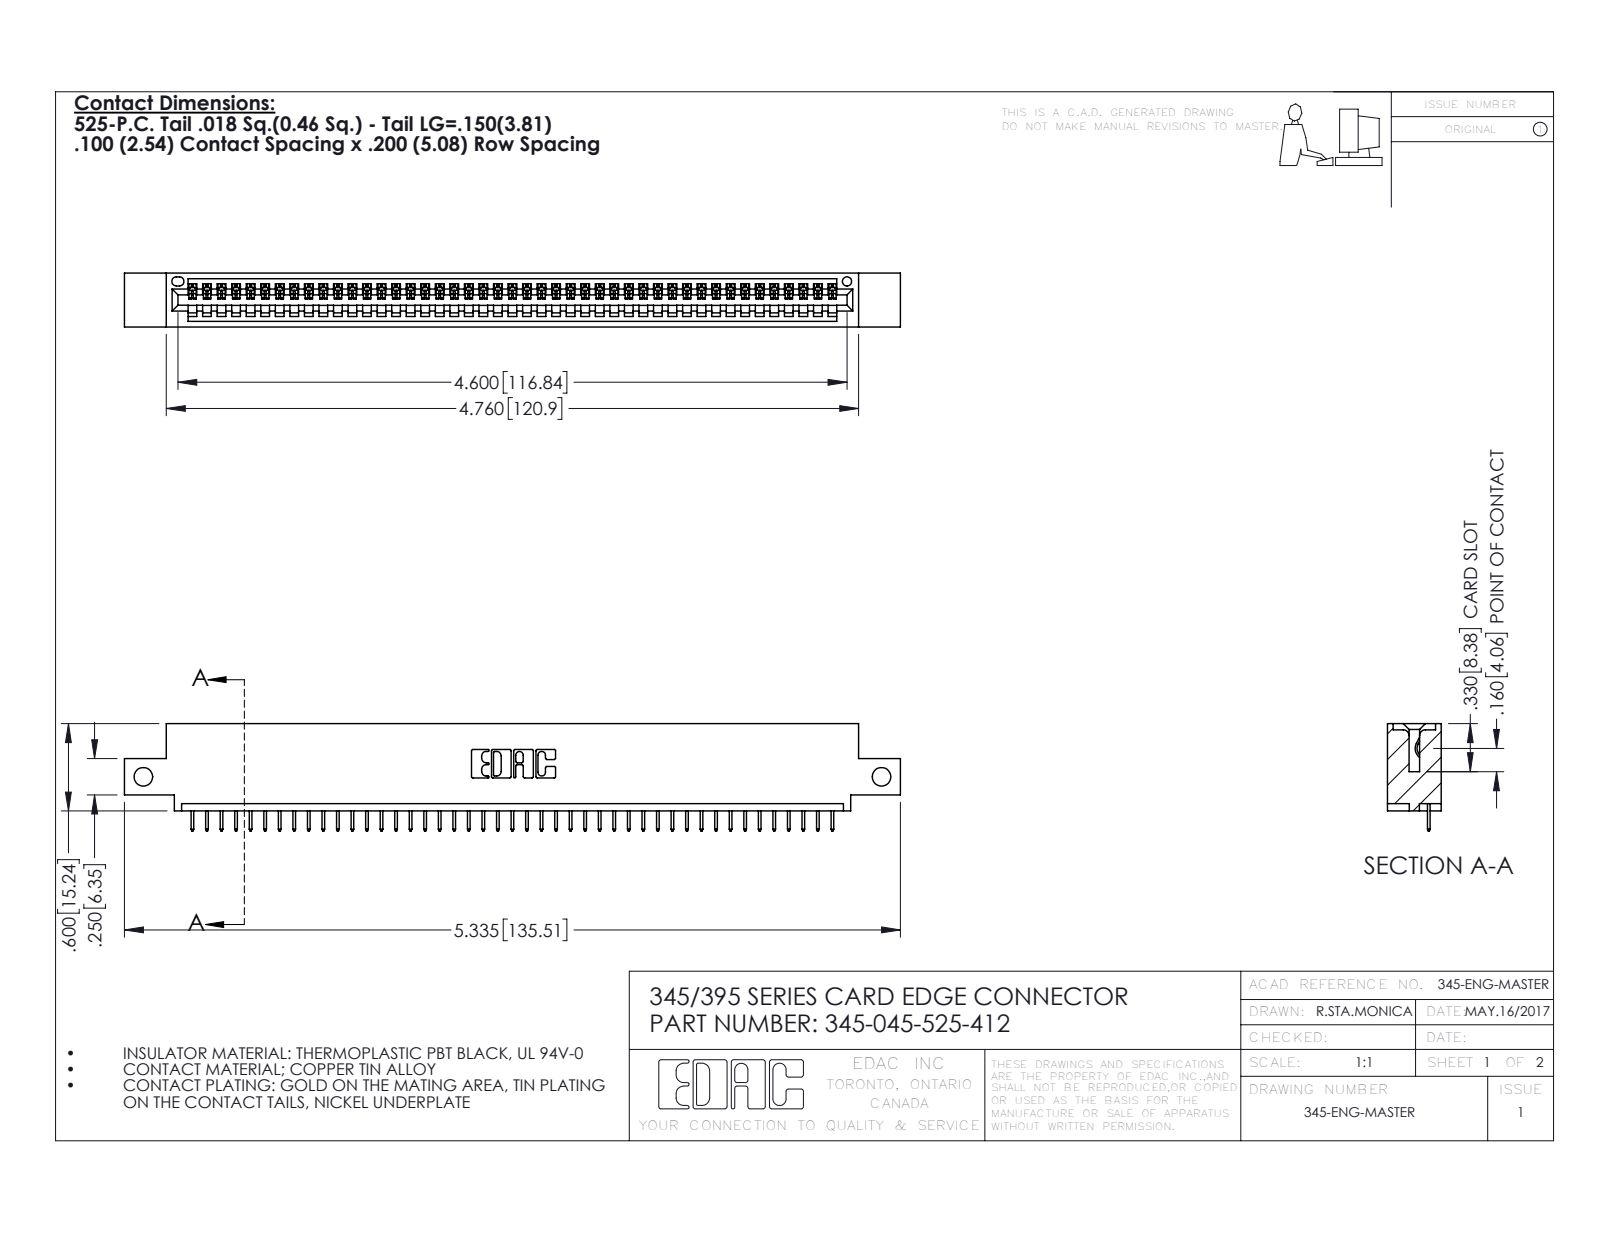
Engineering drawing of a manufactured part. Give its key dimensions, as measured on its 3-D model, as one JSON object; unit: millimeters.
{"part_name": "345-045-525-412; 345 Part_0.110 Offset - Side Mount; 345-292-001_345-293-125", "step_written_by": "SolidWorks 2020 (CONFIG_CONTROL_DESIGN)", "units": "millimeters", "bodies": {"solids": 46, "faces": 2920, "planar": 2154, "cylindrical": 766, "other": 0}, "overall_size": [135.5, 18.7, 9.4], "volume_mm3": 12600, "surface_area_mm2": 16050, "round_holes": [[3.3, 2], [1.6, 1]], "partial_cylinders_radius": [[0.2, 90], [0.3, 22], [0.2, 6], [0.8, 6], [0.7, 3], [0.8, 2], [1, 2], [0.4, 1]], "face_to_face_distances": [1.8, 7.6, 9.4, 5.1, 2.5, 6.9, 0.6, 5.7, 1.8, 3.8], "hole_center_spacings": [128.9]}
